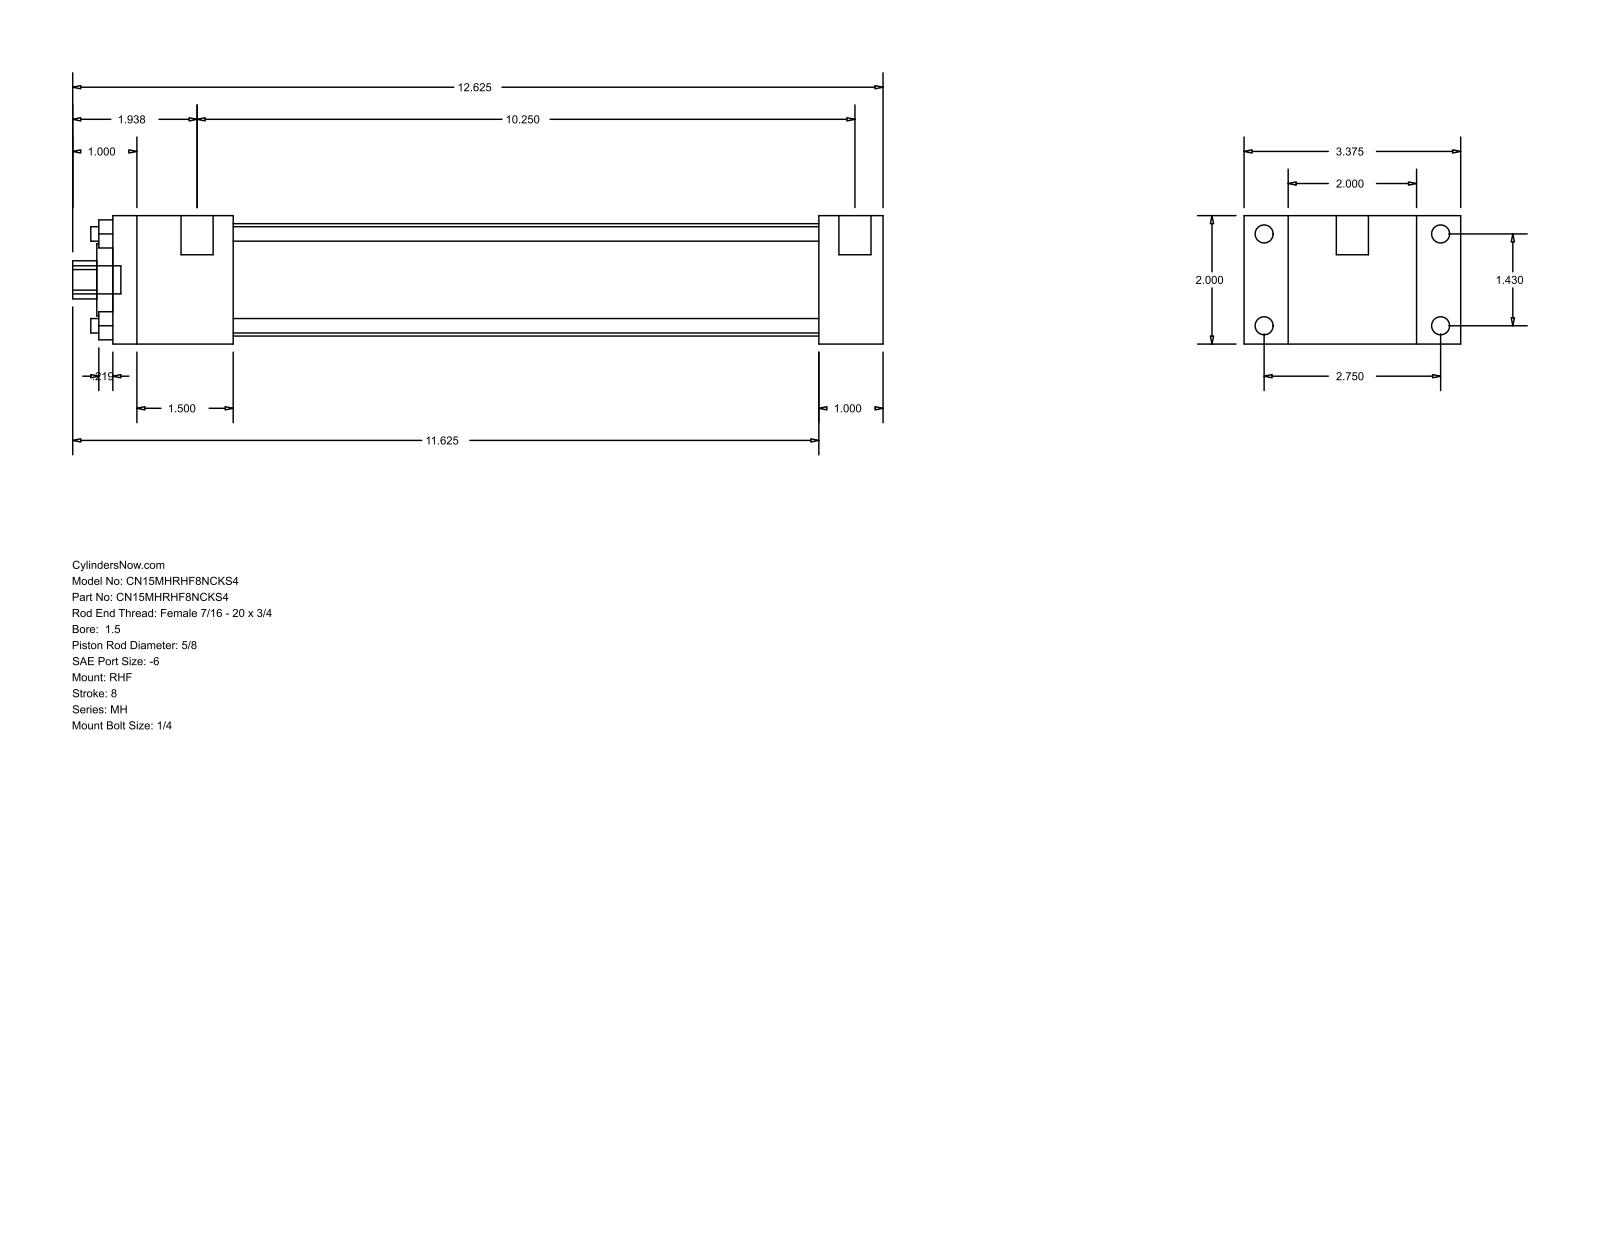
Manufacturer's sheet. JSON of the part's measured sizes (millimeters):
{"part_name": "MH_RHF__0150_0.625", "step_written_by": "GSSL Pune (CONFIG_CONTROL_DESIGN)", "units": "millimeters", "bodies": {"solids": 0, "faces": 88, "planar": 60, "cylindrical": 28, "other": 0}, "overall_size": [320.68, 85.72, 50.8], "round_holes": [[5.71, 4], [15.88, 1], [28.57, 1], [44.45, 1]], "round_bosses_or_shafts": [[7.14, 4], [5.56, 4], [12.7, 2], [11.11, 1]], "partial_cylinders_radius": [[7.54, 1]], "face_to_face_distances": [50.8, 17.46, 68.26, 25.41, 279.39, 304.8, 85.72, 47.62, 231.77, 257.18], "hole_center_spacings": [25.68, 36.32, 51.36]}
